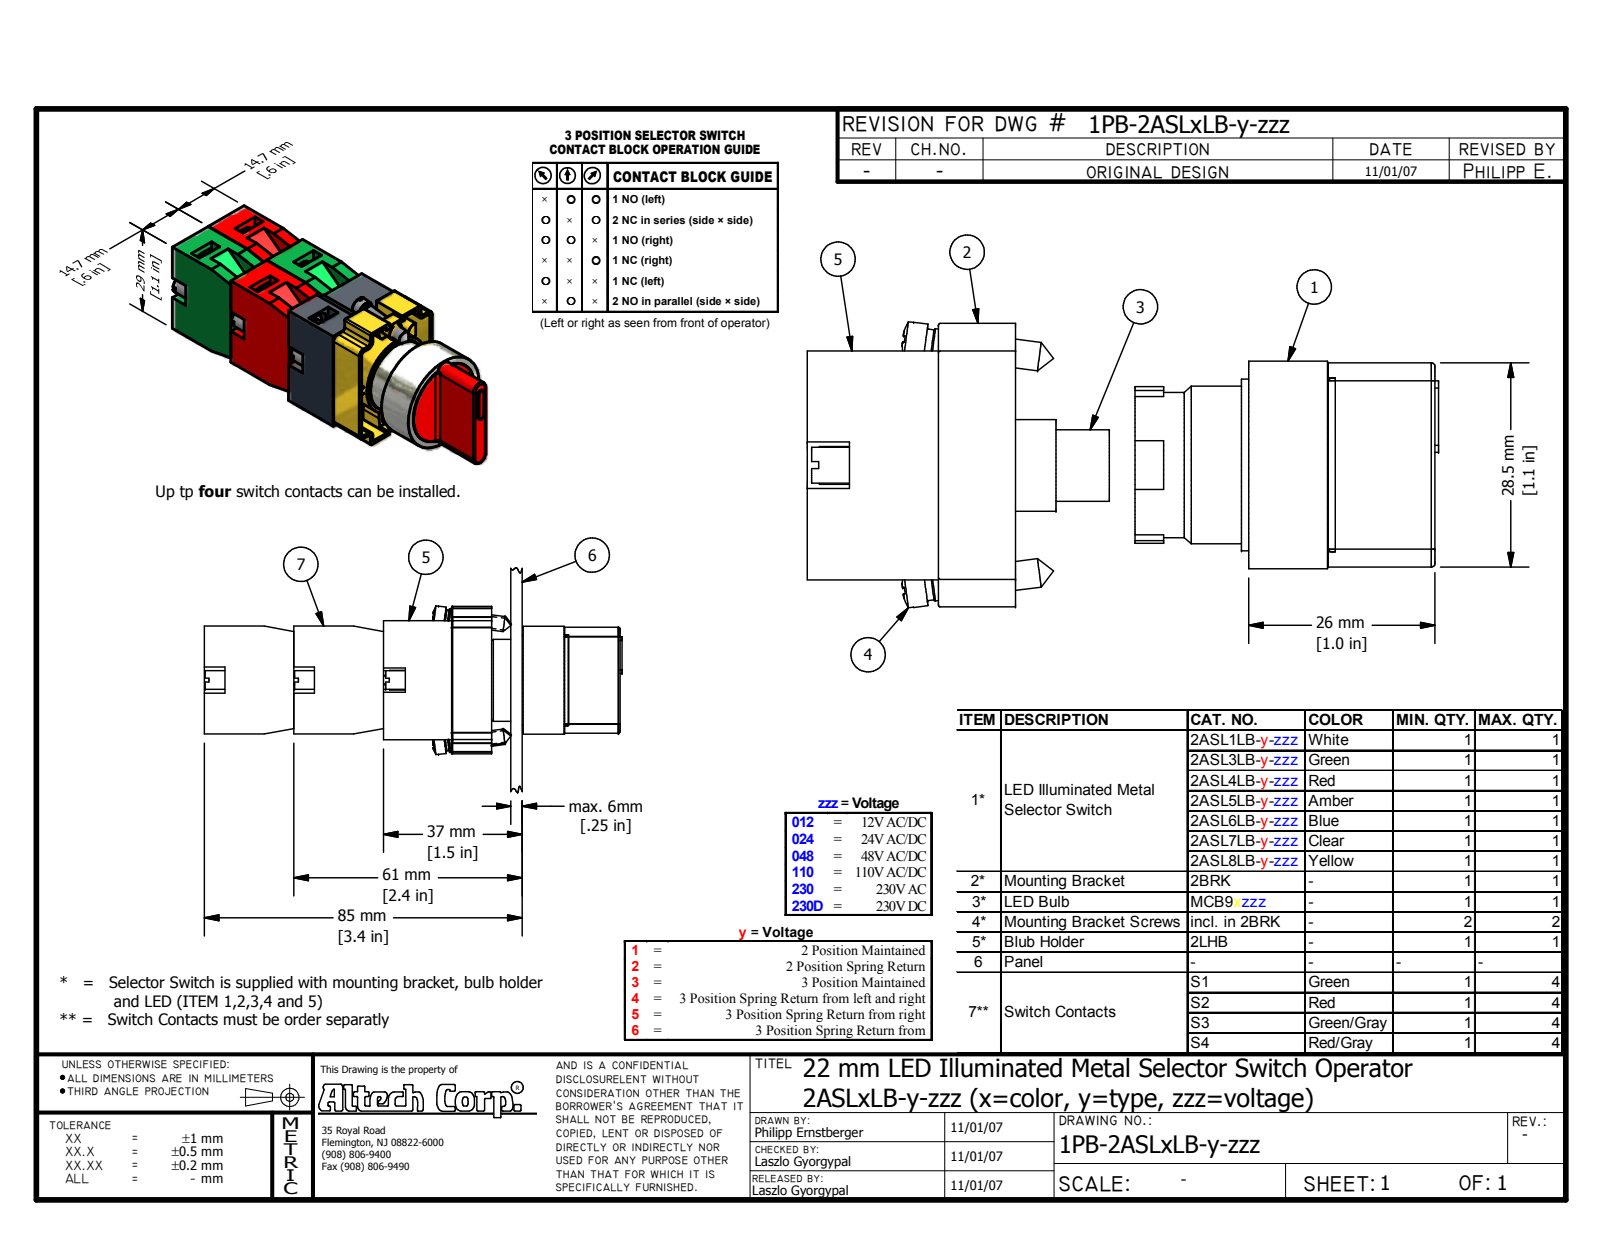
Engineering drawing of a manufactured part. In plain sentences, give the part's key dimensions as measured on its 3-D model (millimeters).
The part is named "2ASLxLBy-zzz_assembly; 2BRK; DIN 7985 (Z) M4x18-Z; S1 (+8 more)". Its 3-D file was written by "Autodesk Inventor 2008 (AUTOMOTIVE_DESIGN)". It is 28 solids with 1105 faces: 596 planar, 187 cylindrical and 322 other. Overall it measures 112.03 by 60.45 by 45 millimeters. Its volume is 73 393 cubic millimeters and its surface area 46 141 square millimeters. Round holes: 5 of diameter 2.5, 2 of diameter 2.6, 1 of diameter 13.5, 1 of diameter 17.75, 1 of diameter 22, 1 of diameter 22.25, 1 of diameter 22.5, 1 of diameter 25, 1 of diameter 27. Round bosses or shafts: 8 of diameter 3, 6 of diameter 2.75, 4 of diameter 5, 4 of diameter 1.5, 2 of diameter 4, 2 of diameter 3.65, 1 of diameter 29, 1 of diameter 24.8. Partial cylindrical surfaces (rounded edges, fillets, slot ends): 18 of radius 1, 10 of radius 0.25, 8 of radius 0.72, 6 of radius 0.5, 5 of radius 2.25, 4 of radius 0.8, 4 of radius 1.8, 4 of radius 2. The main face-to-face distances are 14.8, 14.7, 3, 24, 14.95, 15.05, 29.75, 15.91, 18.91, 29.5. The hole center spacings are 14.53, 6.52, 6.57, 12.05, 12.45, 13, 14.52, 14.55.
